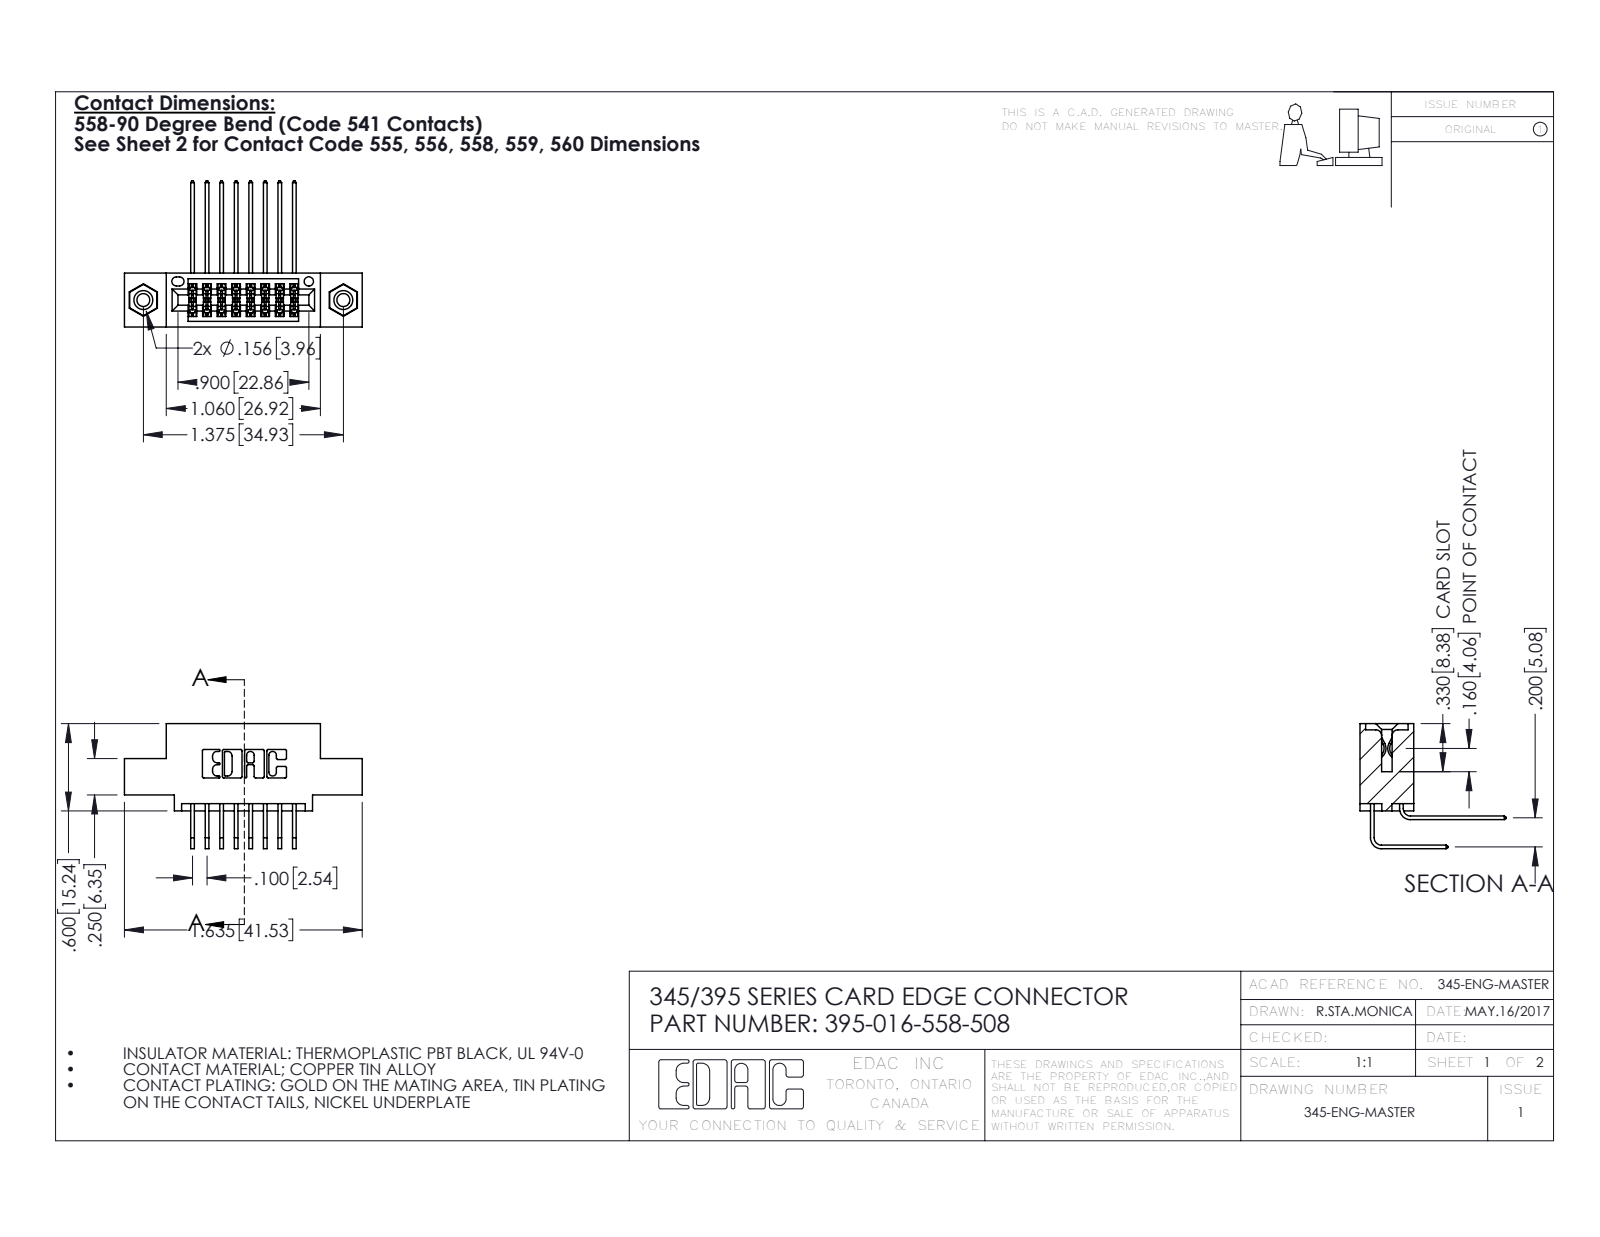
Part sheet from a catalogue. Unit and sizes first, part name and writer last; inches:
Units: inches
Overall size (bounding box): 1.635 × 1.005 × 0.859
Round holes (diameter × count): ⌀0.089 ×2, ⌀0.125 ×2, ⌀0.156 ×2, ⌀0.064 ×1
Round bosses / shafts (diameter × count): ⌀0.155 ×2
Partial cylindrical surfaces — rounded edges, fillets, slot ends (radius × count): R0.006 ×25, R0.01 ×22, R0.007 ×6, R0.031 ×6, R0.026 ×3, R0.014 ×2, R0.019 ×2, R0.022 ×2
Main face-to-face distances: 0.2, 0.072, 0.298, 0.37, 0.1, 0.3, 0.098, 0.272, 0.025, 0.16
Hole centre spacings: 0.27, 1.144, 1.375
Volume: 0.228 in³ · Surface area: 8.365 in²
Bodies: 19 solids, 1022 faces (676 planar, 330 cylindrical, 16 other)
Part name (STEP PRODUCT): 345-292-001_558 559 Tail - 1; 345 Part_0.110 Offset - 0.156 Dia-TI; 345-292-001_558 Tail - 2; 345-250-001_345-250-003-102 (+1 more)
STEP written by: SolidWorks 2016 (CONFIG_CONTROL_DESIGN)
